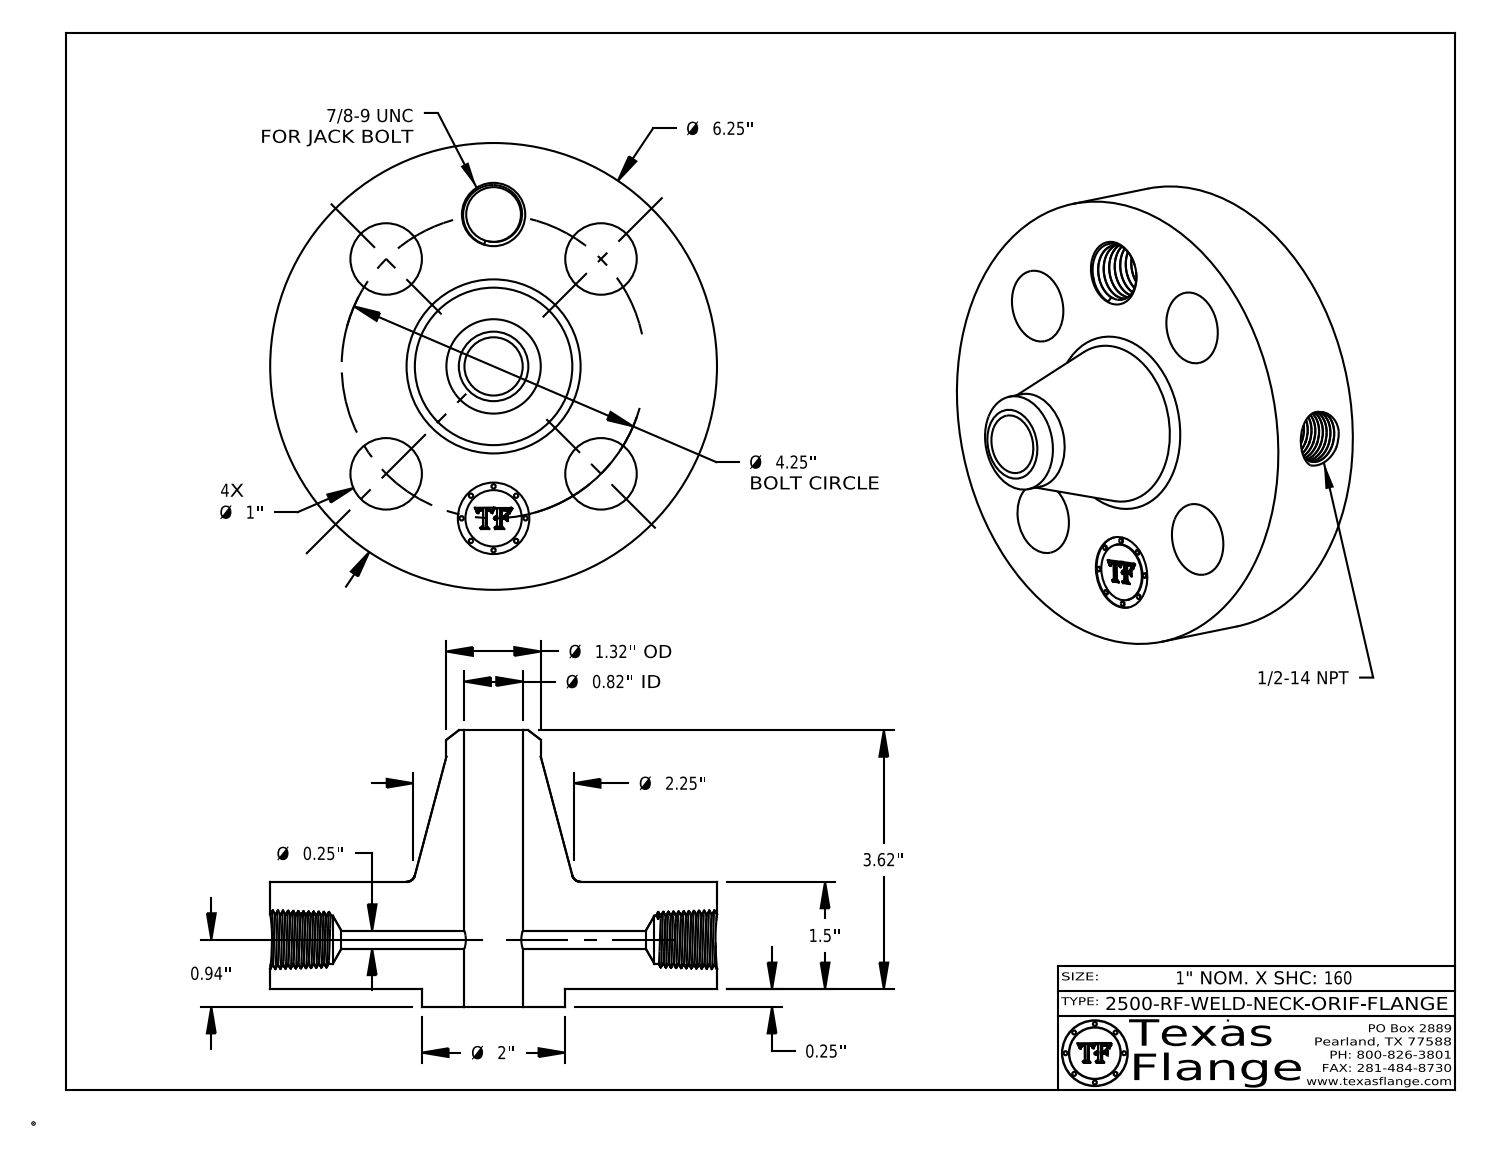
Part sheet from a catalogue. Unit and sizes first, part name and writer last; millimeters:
Units: millimetres
Overall size (bounding box): 158.8 × 158.8 × 98.3
Round holes (diameter × count): ⌀25.4 ×5, ⌀6.4 ×1, ⌀17.1 ×1, ⌀19.5 ×1, ⌀20.7 ×1
Round bosses / shafts (diameter × count): ⌀1.5 ×8, ⌀158.8 ×1, ⌀50.8 ×1, ⌀33.5 ×1, ⌀20 ×1
Main face-to-face distances: 38.1, 6.4, 44.5, 0.4, 44.1, 37.7, 98.3, 91.9, 54.2, 53.8
Hole centre spacings: 54, 41.3, 76.4, 99.7, 108
Volume: 709 200 mm³ · Surface area: 87 940 mm²
Bodies: 1 solid, 751 faces (369 planar, 82 cylindrical, 300 other)
Part name (STEP PRODUCT): 2500-RF-WELD-NECK
STEP written by: CATIA V5 STEP AP214 (AUTOMOTIVE_DESIGN)
